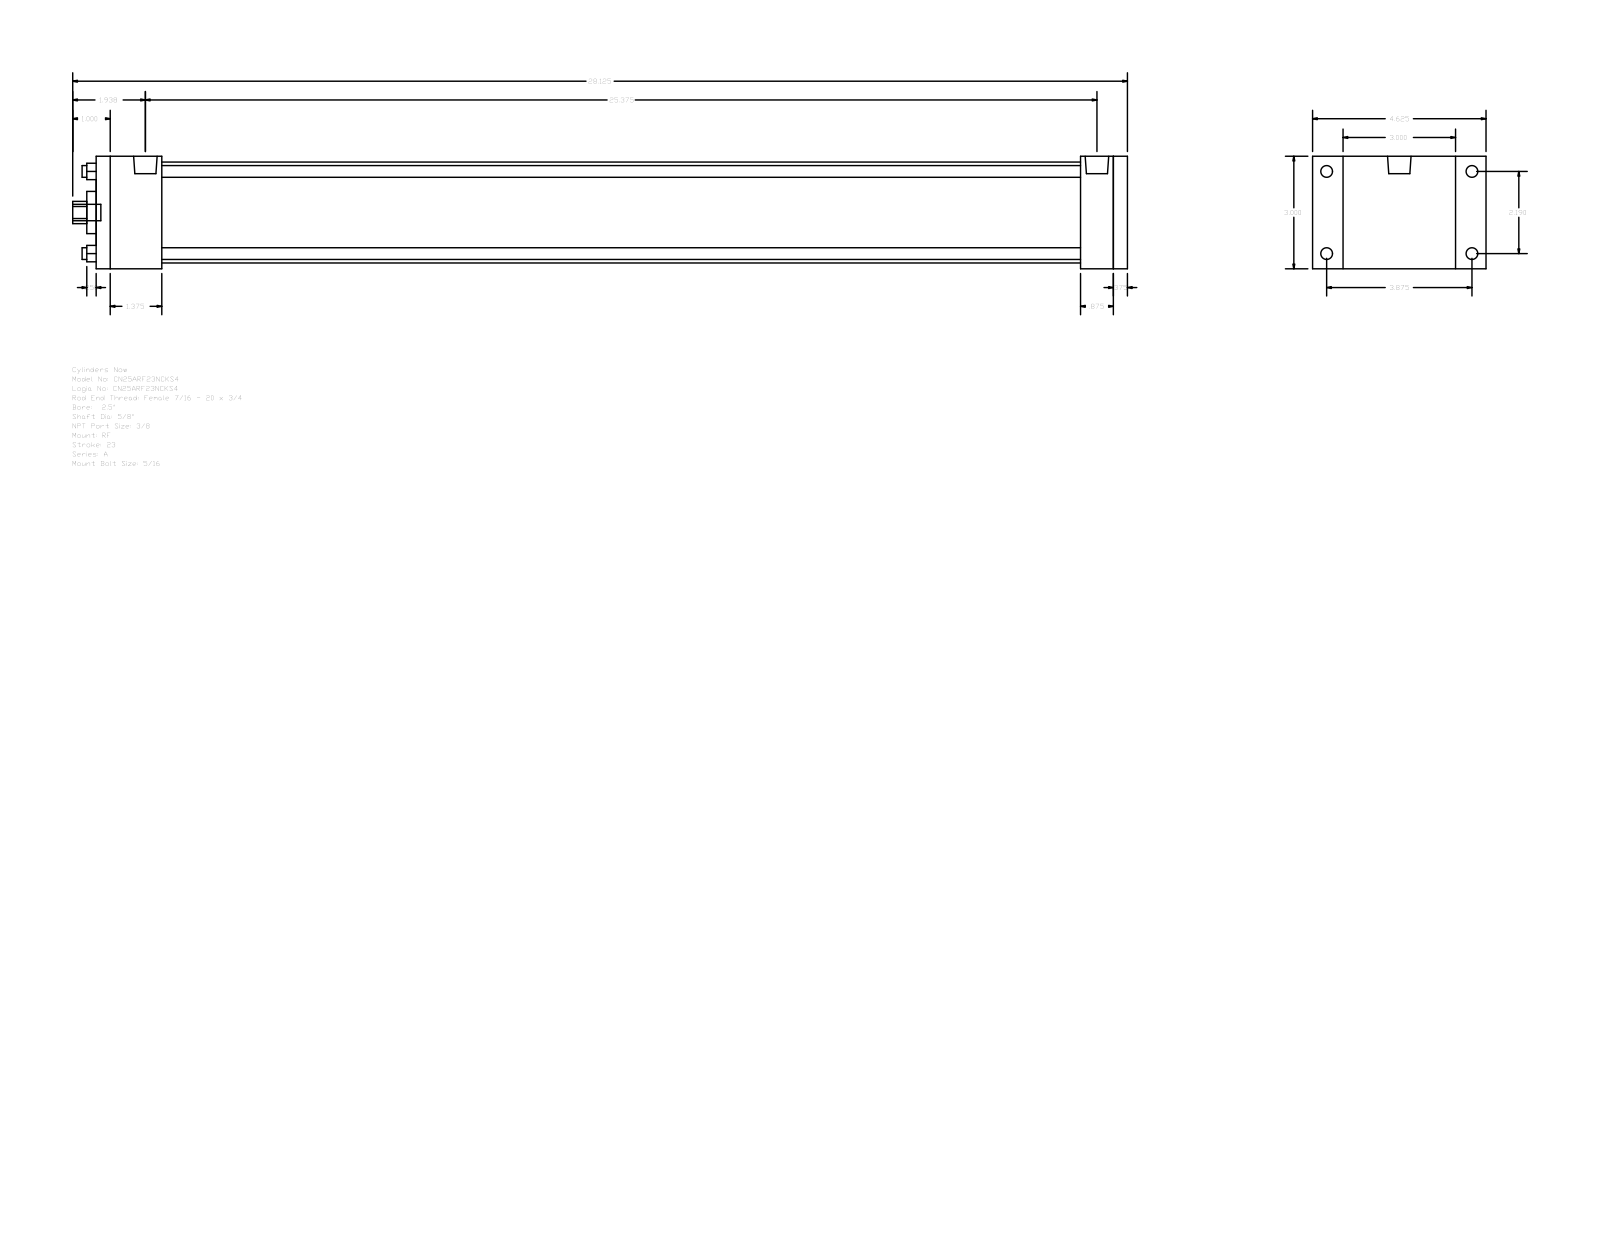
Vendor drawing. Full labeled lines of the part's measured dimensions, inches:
Part name (STEP PRODUCT): A_RF__0250_0.625
STEP written by: GSSL Pune (CONFIG_CONTROL_DESIGN)
Units: inches
Bodies: 0 solids, 92 faces (64 planar, 28 cylindrical, 0 other)
Overall size (bounding box): 28.125 × 4.625 × 3
Round holes (diameter × count): ⌀0.313 ×4, ⌀0.625 ×1, ⌀1.125 ×1, ⌀2.69 ×1
Round bosses / shafts (diameter × count): ⌀0.313 ×4, ⌀0.219 ×4, ⌀0.627 ×2, ⌀0.437 ×1
Partial cylindrical surfaces — rounded edges, fillets, slot ends (radius × count): R0.297 ×1
Main face-to-face distances: 3, 27.5, 0.375, 27.125, 1.75, 26.25, 24.5, 25.375, 25.75, 0.875
Hole centre spacings: 1.548, 2.19, 3.097
